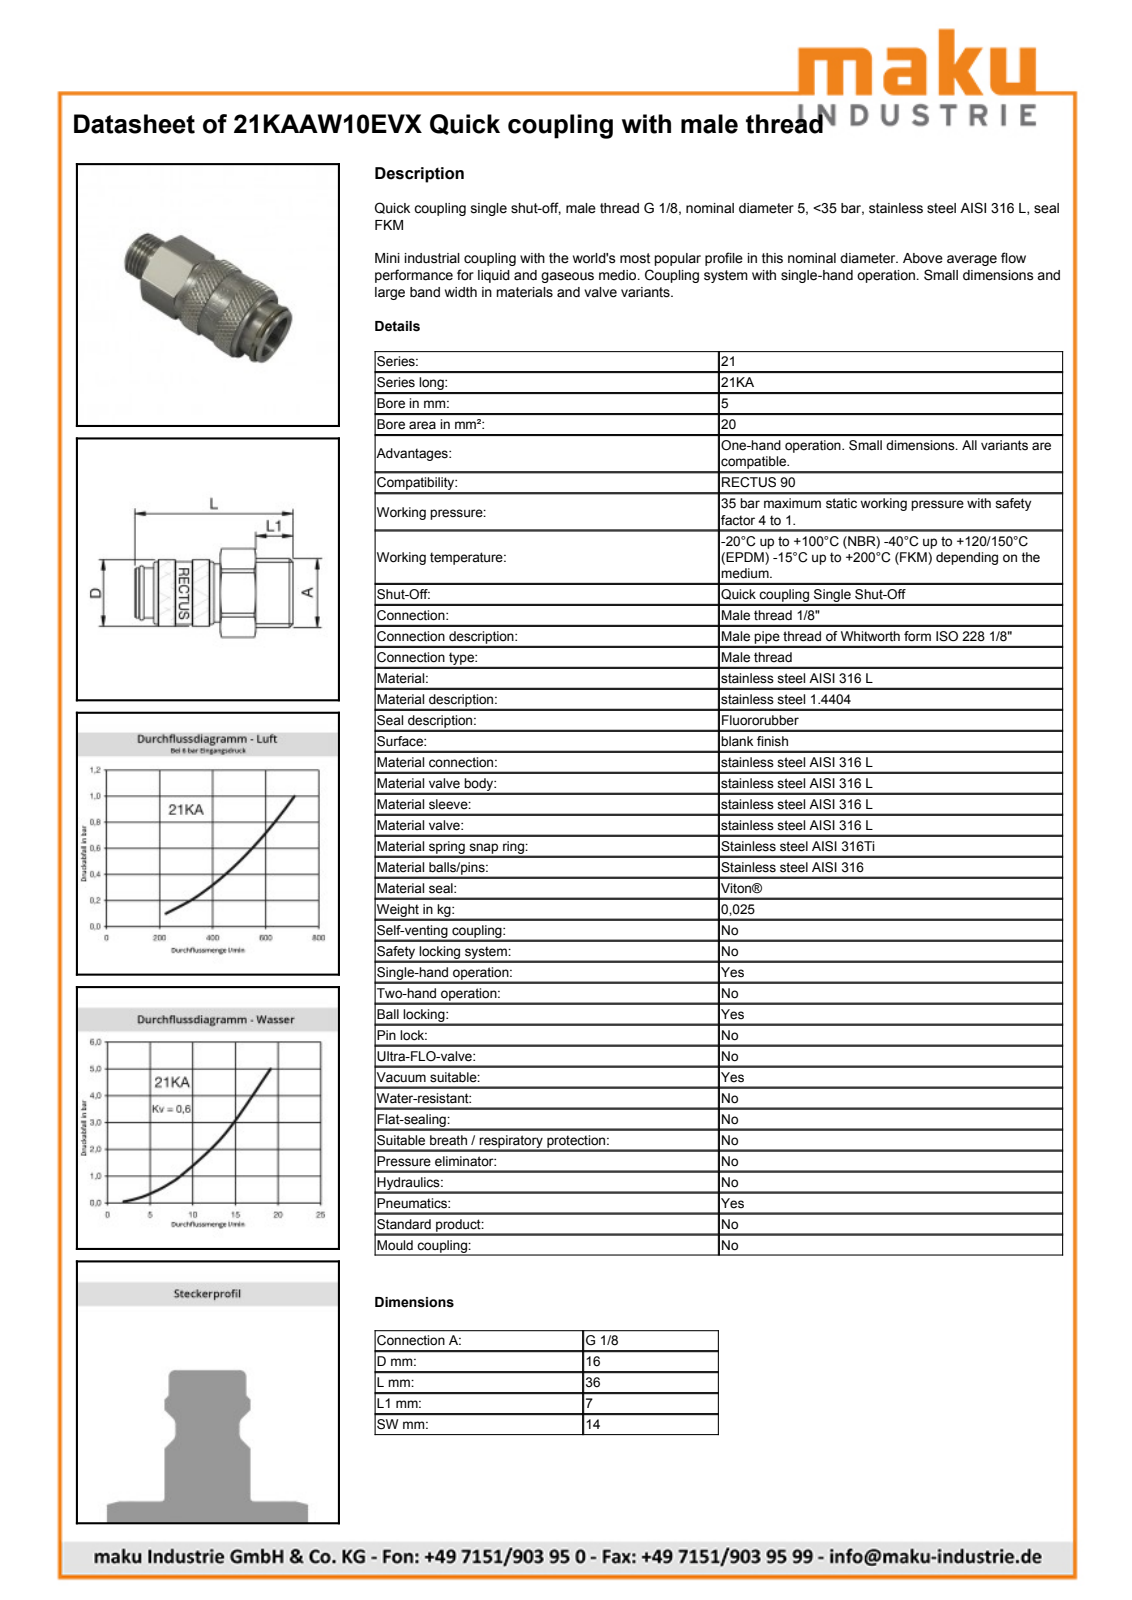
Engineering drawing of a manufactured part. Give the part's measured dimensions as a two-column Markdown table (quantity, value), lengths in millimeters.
| quantity | value |
| --- | --- |
| part name | D110762 |
| STEP written by | Autodesk Inventor 2013 (AUTOMOTIVE_DESIGN) |
| units | millimeters |
| bodies | 2 solids, 401 faces (163 planar, 64 cylindrical, 174 other) |
| overall size | 36.15 × 16.15 × 16.15 |
| volume | 5 169 mm³ |
| surface area | 3 383 mm² |
| round holes (diameter × count) | 12.15 × 1, 14 × 1 |
| round bosses / shafts (diameter × count) | 16.15 × 1, 15.1 × 1, 12 × 1, 11.4 × 1, 11.15 × 1, 10.99 × 1, 9.73 × 1 |
| partial cylindrical surfaces (radius × count) | 7.45 × 1, 7.9 × 1 |
| main face-to-face distances | 14, 29.15, 36.15, 7, 16.15, 13, 20, 4.56, 11.59, 24.59 |
